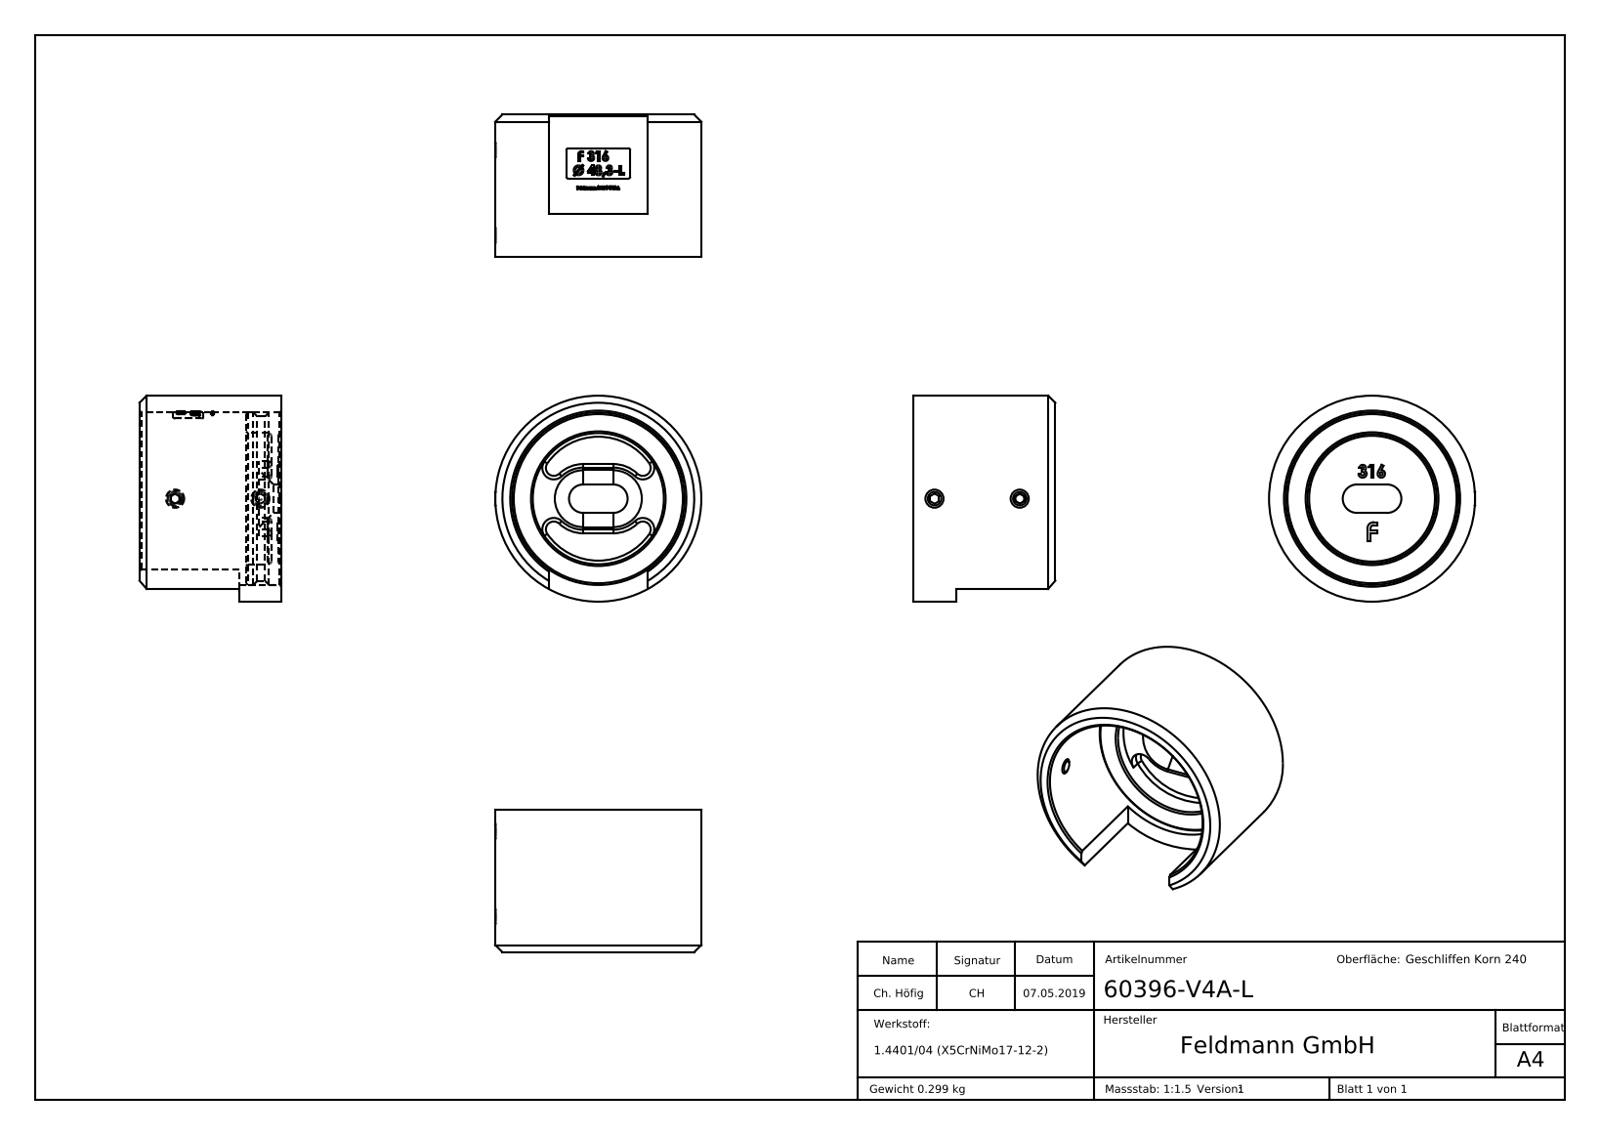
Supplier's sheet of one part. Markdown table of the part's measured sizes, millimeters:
| quantity | value |
| --- | --- |
| part name | DIN914_DIN 914 M5x6; 60396-V4A-L; 6039X-240-X Teil2_60396-V4A-X Teil2; DIN913_DIN 913 M5x5 (+1 more) |
| STEP written by | SolidWorks 2015 (CONFIG_CONTROL_DESIGN) |
| units | millimeters |
| bodies | 4 solids, 564 faces (243 planar, 85 cylindrical, 236 other) |
| overall size | 58 × 58 × 40 |
| volume | 37 345 mm³ |
| surface area | 19 797 mm² |
| round holes (diameter × count) | 4.2 × 2, 36.9 × 1, 48.6 × 1 |
| round bosses / shafts (diameter × count) | 5 × 2, 58 × 1, 46.34 × 1 |
| partial cylindrical surfaces (radius × count) | 0.5 × 4, 3.22 × 4, 1 × 2, 4 × 2, 8.75 × 2, 24.4 × 1, 24.5 × 1 |
| main face-to-face distances | 1, 10, 9, 2.8, 1.8, 7.2, 40, 39, 37.2, 30 |
| hole center spacings | 24 |
